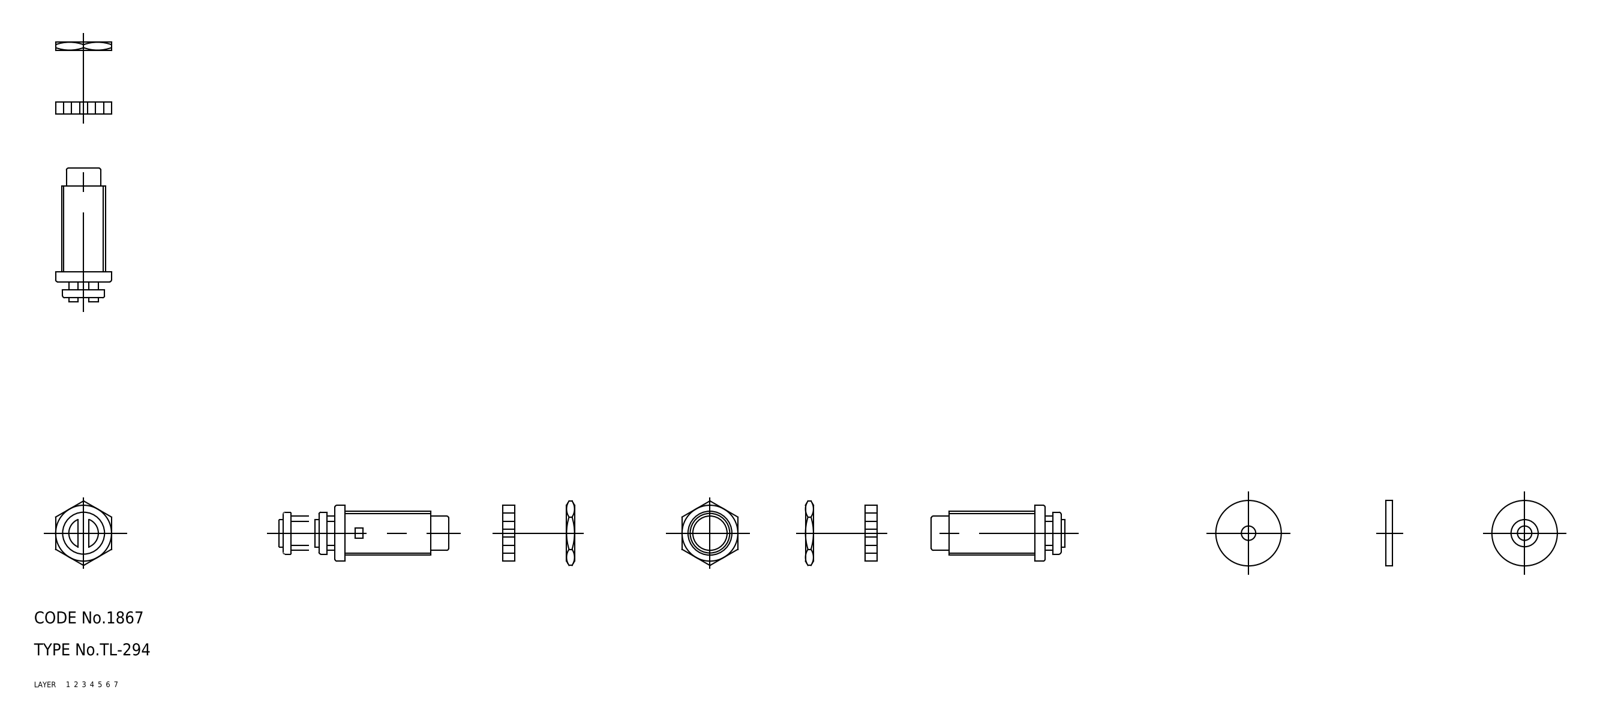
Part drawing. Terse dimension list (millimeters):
name: keeper; attachment; spacer; nut (+4 more)
written by: CADfix (AUTOMOTIVE_DESIGN)
unit: mm
bodies: 8 solids, 91 faces (0 planar, 0 cylindrical, 91 other)
size: 54.43 × 16.4 × 16.4
volume: 3 382 mm³; area: 3 674 mm²
